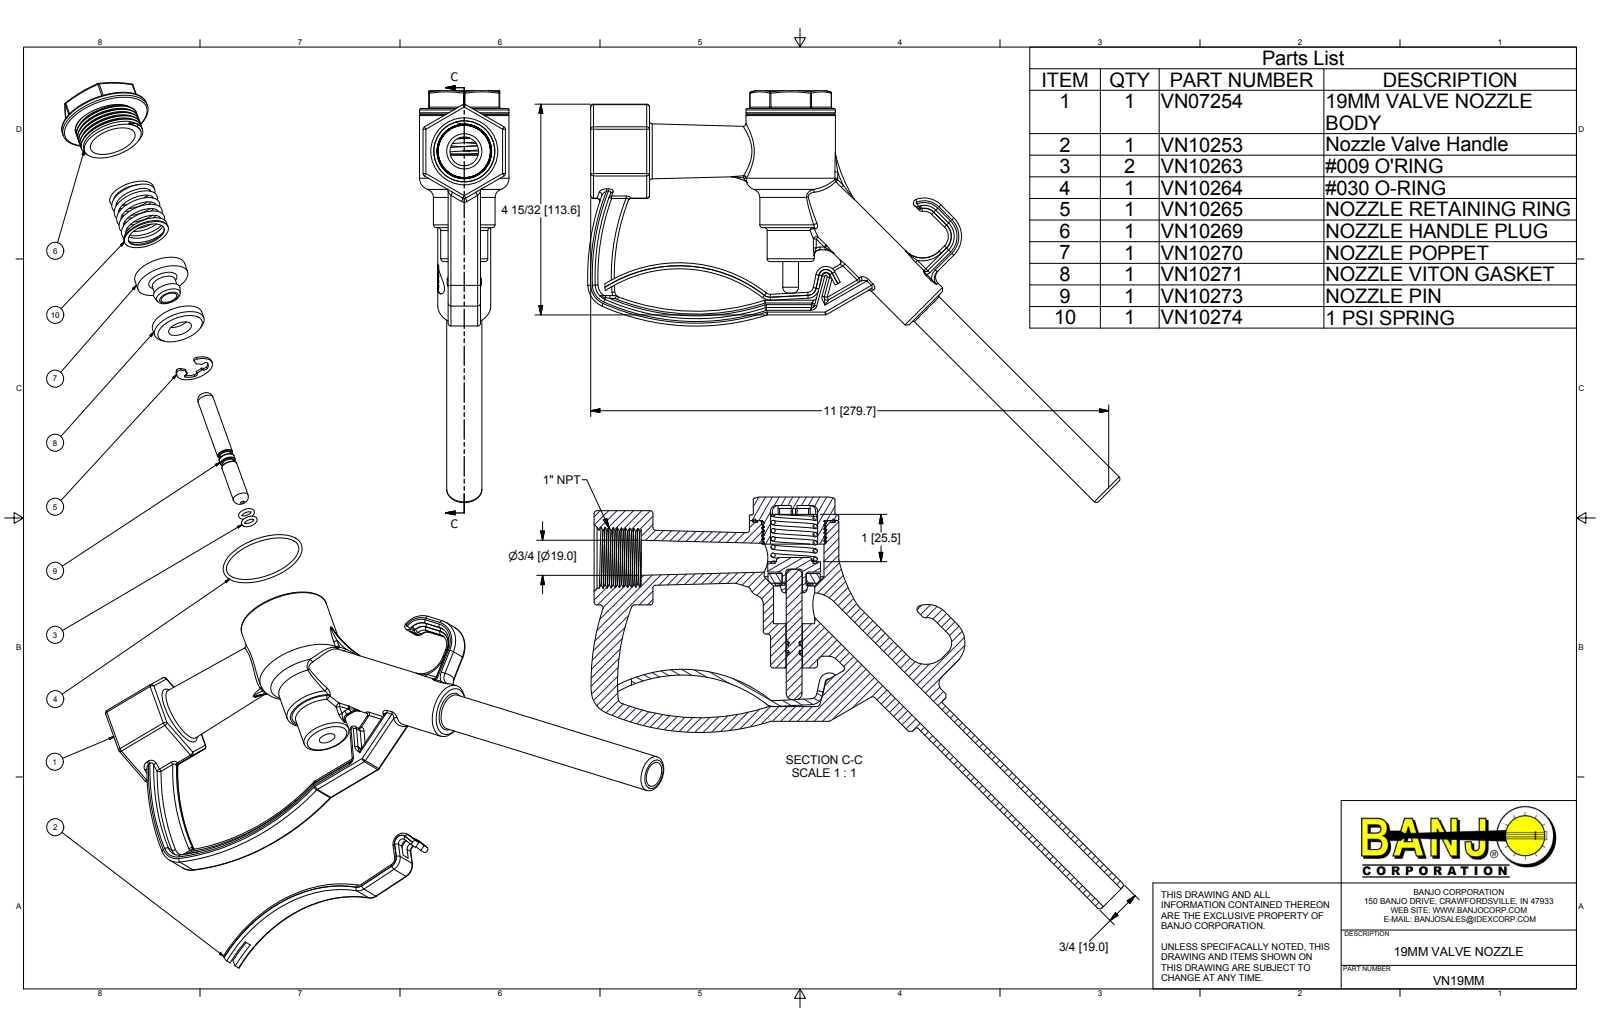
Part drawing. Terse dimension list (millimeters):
name: VN07254; VN10264; VN10269; VN10271 (+7 more)
written by: Autodesk Inventor 2016 (AUTOMOTIVE_DESIGN)
unit: mm
bodies: 11 solids, 887 faces (319 planar, 267 cylindrical, 301 other)
size: 287.33 × 222.35 × 48.26
volume: 240 688 mm³; area: 100 251 mm²
holes: 2× ⌀19.05, 1× ⌀3.15, 1× ⌀4.45, 1× ⌀8.89, 1× ⌀12.95, 1× ⌀13.46, 1× ⌀22.22, 1× ⌀25.4, 1× ⌀32.26, 1× ⌀32.86, 1× ⌀35.15, 1× ⌀44.45
bosses: 1× ⌀48.26, 1× ⌀39.37, 1× ⌀34.55, 1× ⌀28.58, 1× ⌀28.45, 1× ⌀28.19, 1× ⌀19, 1× ⌀8.46
rounds: 96× R1.52, 14× R0.76, 6× R1.41, 4× R1.27, 3× R1.98, 3× R3.17, 2× R0.45, 2× R0.57
face distances: 12.7, 44.45, 20.24, 24.2, 6.75, 25.4, 44.44, 4.76, 3.96, 13.49
hole spacings: 6.59
